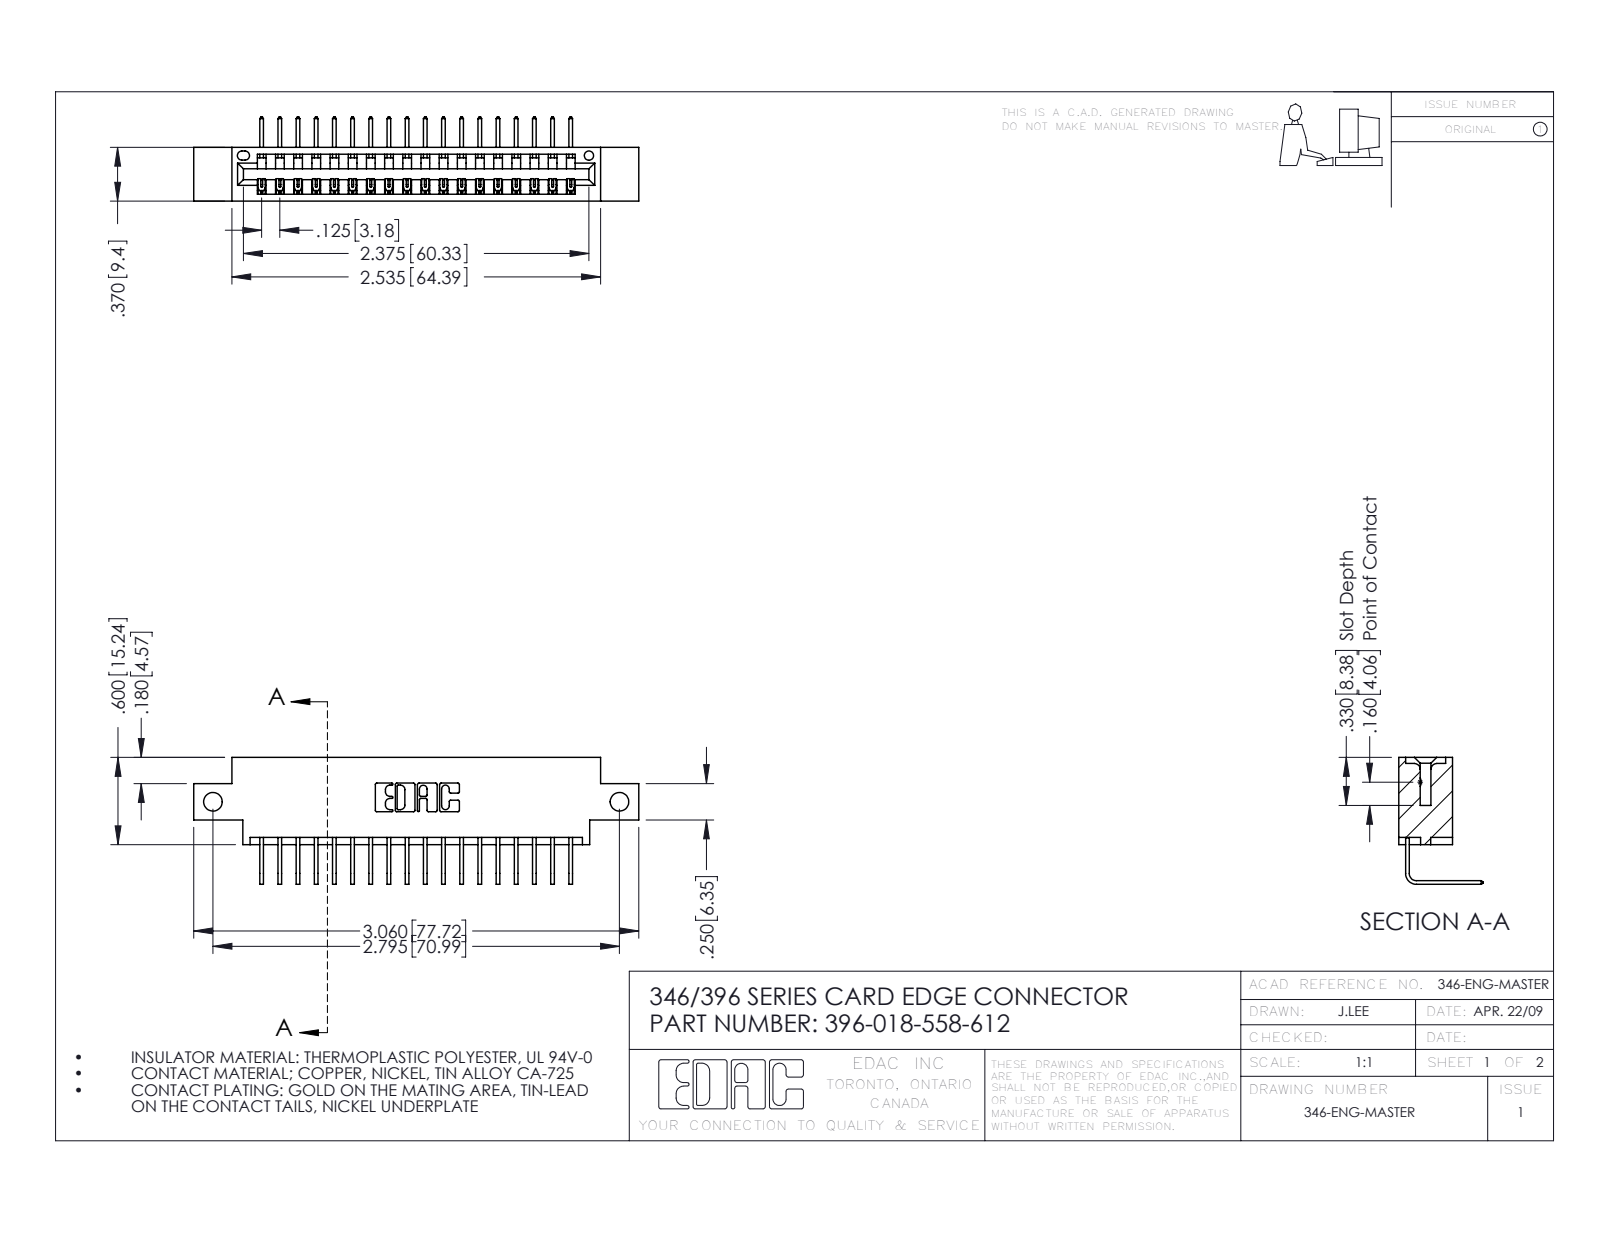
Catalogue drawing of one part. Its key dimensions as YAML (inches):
part_name: "396-018-558-612; 346 Part_0.170 Offset - Side Mount; 345-292-001_558 Tail - 2"
step_written_by: "SolidWorks 2016 (CONFIG_CONTROL_DESIGN)"
units: inches
bodies: {solids: 19, faces: 1206, planar: 836, cylindrical: 370, other: 0}
overall_size: [3.06, 0.873, 0.58]
volume: 0.433
surface_area: 13.92
round_holes:
  - {diameter: 0.128, count: 2}
  - {diameter: 0.064, count: 1}
partial_cylinders:
  - {radius: 0.006, count: 36}
  - {radius: 0.01, count: 22}
  - {radius: 0.007, count: 6}
  - {radius: 0.031, count: 6}
  - {radius: 0.026, count: 3}
  - {radius: 0.031, count: 2}
  - {radius: 0.04, count: 2}
  - {radius: 0.014, count: 1}
face_to_face_distances: [0.322, 0.048, 0.37, 0.25, 0.298, 0.025, 0.072, 0.148, 0.222, 0.1]
hole_center_spacings: [2.795]
